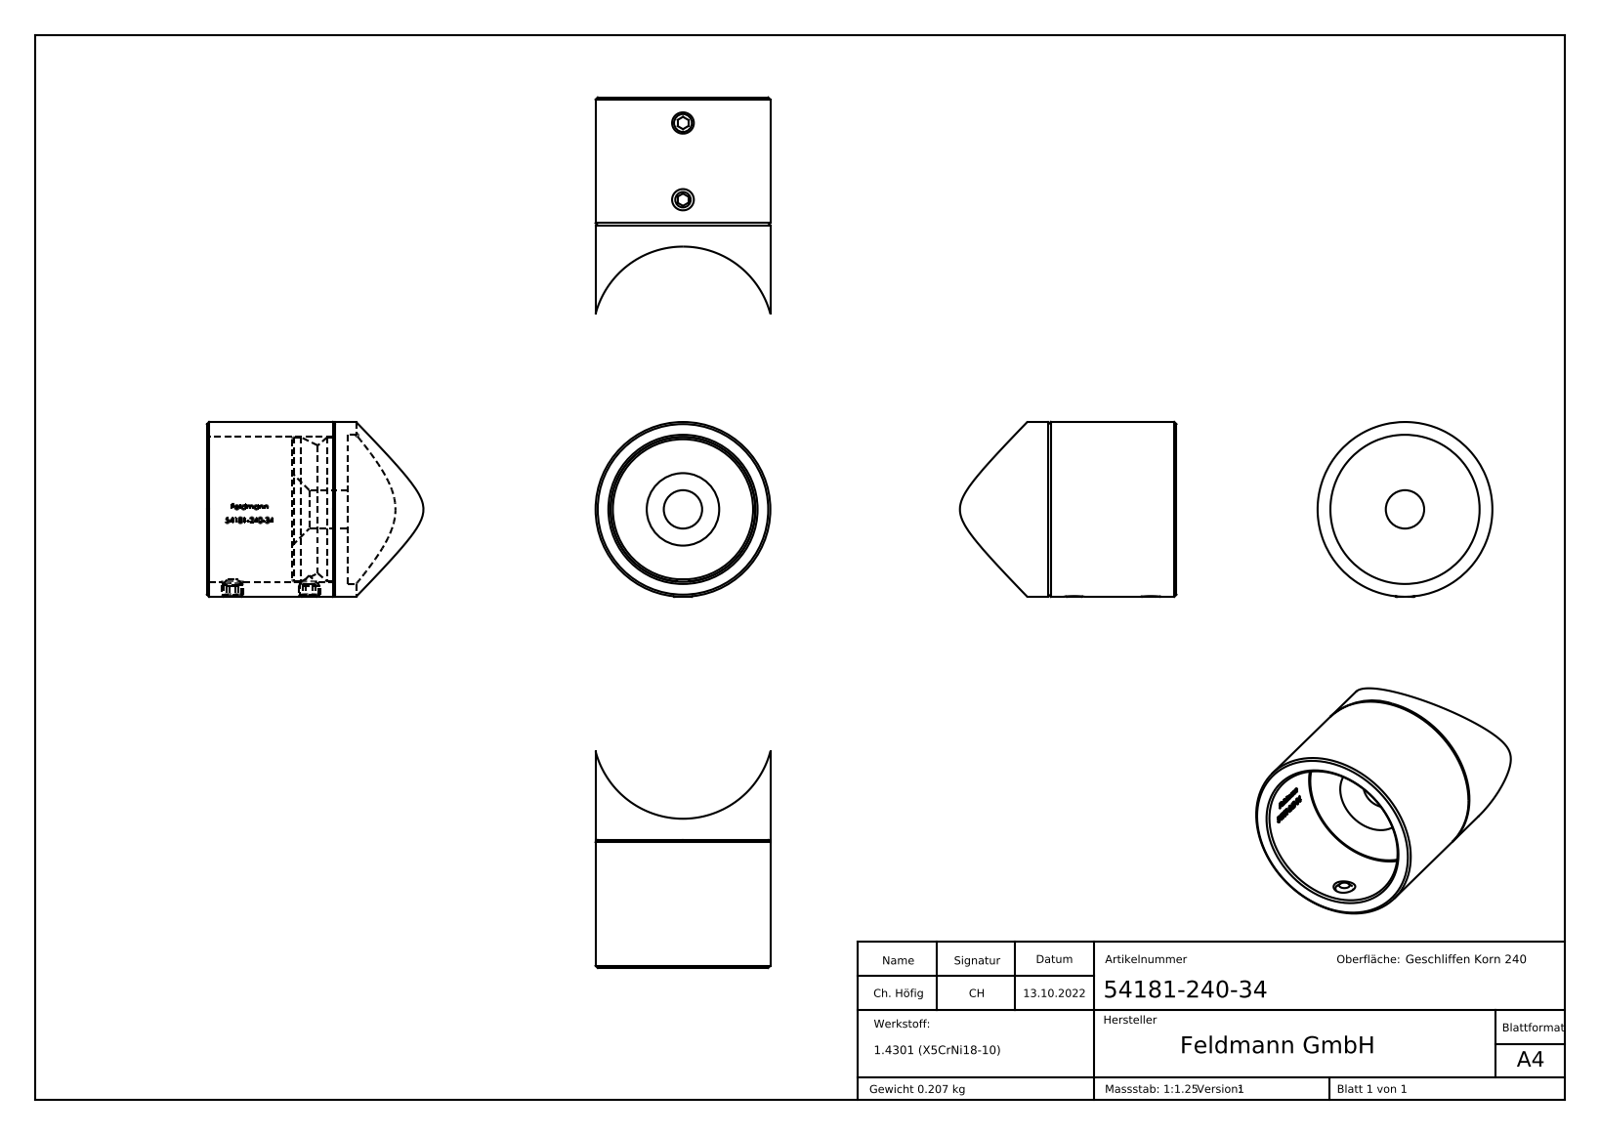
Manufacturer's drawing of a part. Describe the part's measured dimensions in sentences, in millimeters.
The part is named "DIN 914 M5xX_DIN914 M5x5; 54181-240-34; 54181-240-XX Teil2_54181-240-34 Teil2; DIN913 M5xX_DIN913 M5x4 (+1 more)". Its 3-D file was written by "SolidWorks 2018 (CONFIG_CONTROL_DESIGN)". It is 4 solids with 308 faces: 150 planar, 41 cylindrical and 117 other. Overall it measures 50.8 by 41 by 41 millimeters. Its volume is 26 112 cubic millimeters and its surface area 14 325 square millimeters. Round holes: 2 of diameter 4.2, 1 of diameter 9, 1 of diameter 34, 1 of diameter 35. Round bosses or shafts: 2 of diameter 5, 1 of diameter 41, 1 of diameter 33.9. Partial cylindrical surfaces (rounded edges, fillets, slot ends): 1 of radius 17.1, 1 of radius 21.2. The main face-to-face distances are 3, 13, 10, 33, 30, 20, 2.5, 15.58, 18.08, 13.08. The hole center spacings are 18.
